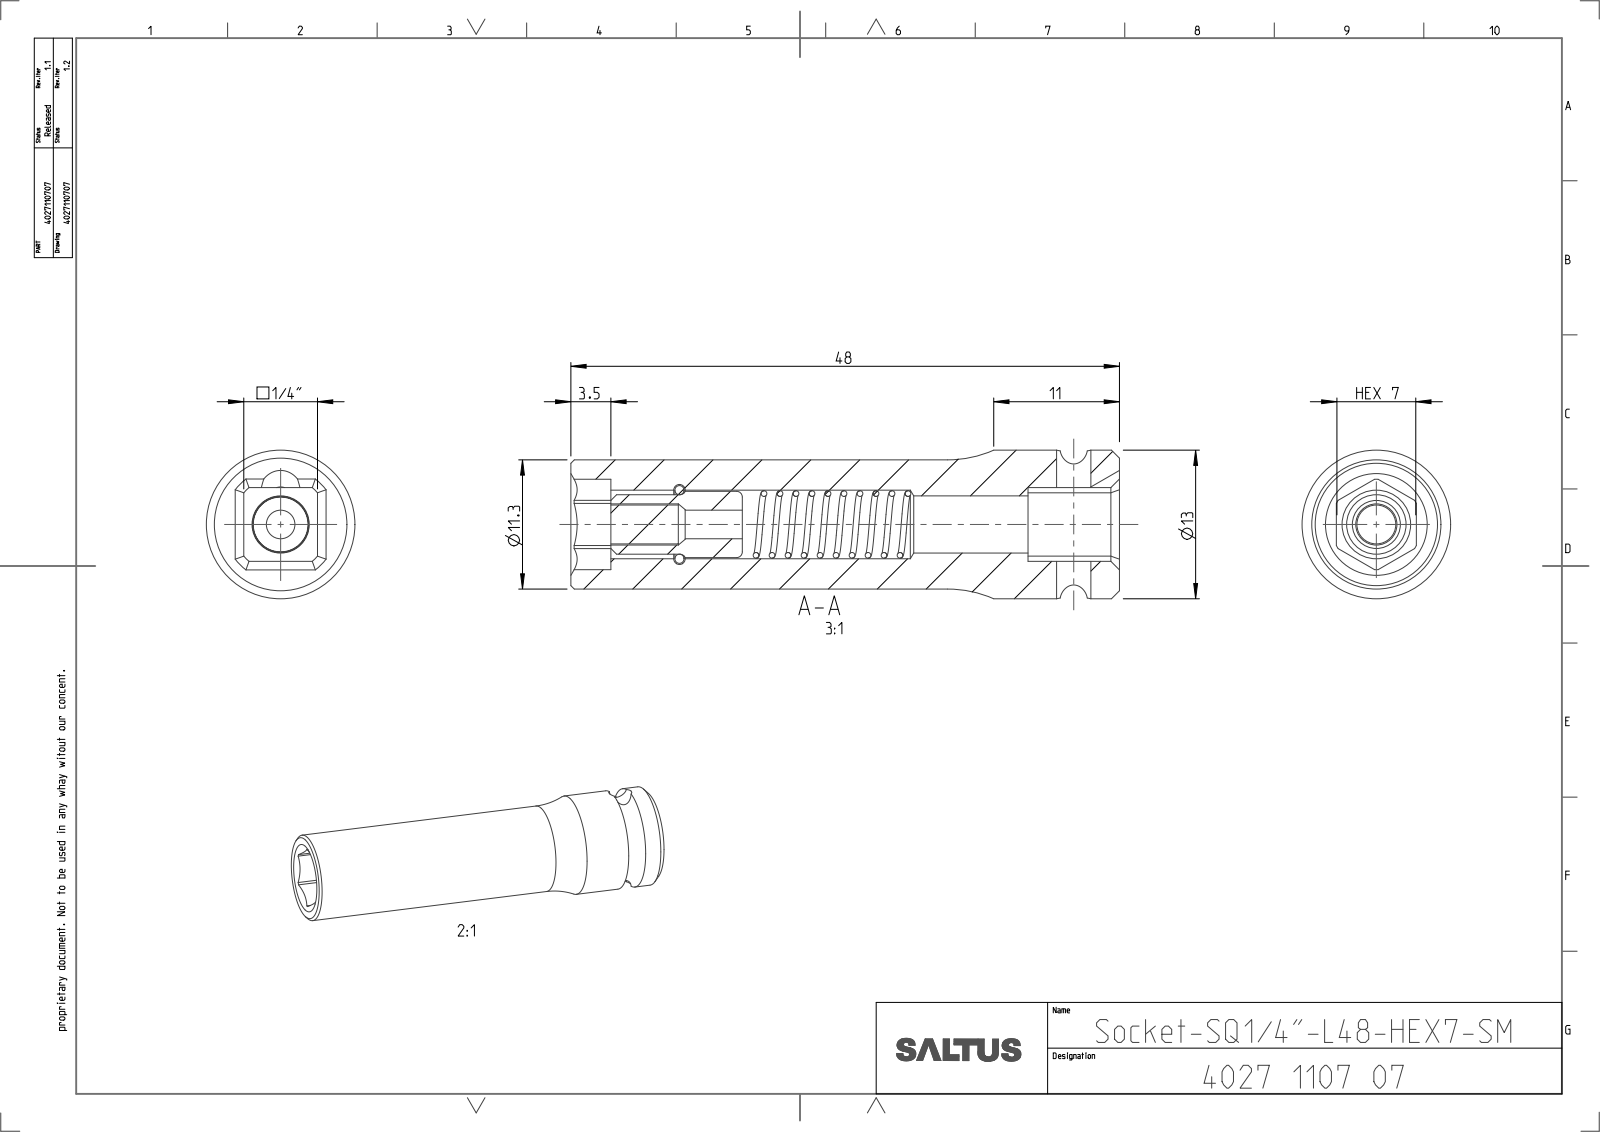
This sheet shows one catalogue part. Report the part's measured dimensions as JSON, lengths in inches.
{"part_name": "4027110707", "step_written_by": "CREO PARAMETRIC BY PTC INC, 2022414 (CONFIG_CONTROL_DESIGN)", "units": "inches", "bodies": {"solids": 4, "faces": 99, "planar": 26, "cylindrical": 37, "other": 36}, "overall_size": [1.89, 0.512, 0.512], "volume_in3": 0.24, "surface_area_in2": 5.667, "round_holes": [[0.098, 1], [0.118, 1], [0.142, 1], [0.197, 1], [0.236, 1]], "round_bosses_or_shafts": [[0.512, 1], [0.445, 1], [0.228, 1], [0.205, 1], [0.134, 1]], "partial_cylinders_radius": [[0.079, 1], [0.156, 1], [0.167, 1]], "face_to_face_distances": [0.254, 0.276, 1.89, 0.138, 1.752, 0.265, 0.315, 1.437, 1.575, 1.299]}
